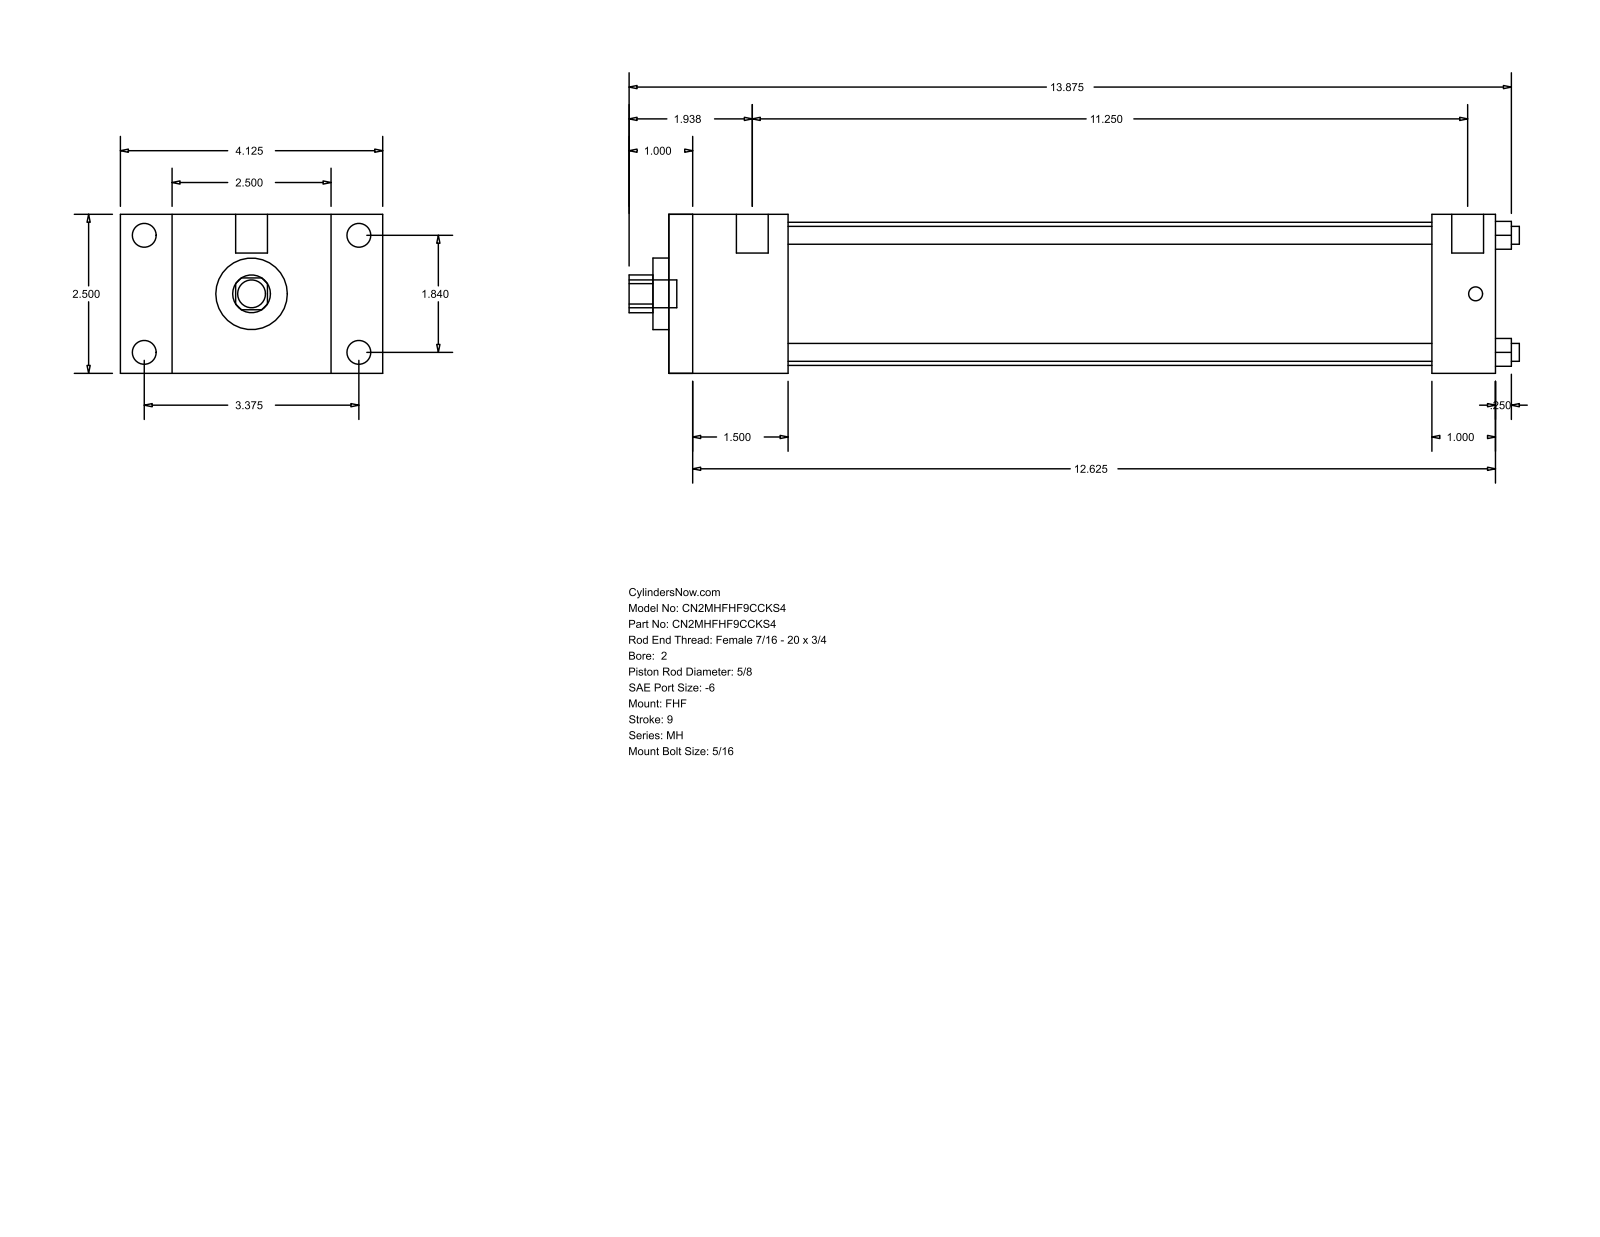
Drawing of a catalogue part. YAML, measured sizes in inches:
part_name: "MH_FHF__0200_0.625"
step_written_by: "GSSL Pune (CONFIG_CONTROL_DESIGN)"
units: inches
bodies: {solids: 0, faces: 88, planar: 60, cylindrical: 28, other: 0}
overall_size: [14, 4.125, 2.5]
round_holes:
  - {diameter: 0.281, count: 4}
  - {diameter: 0.625, count: 1}
  - {diameter: 1.125, count: 1}
  - {diameter: 2.25, count: 1}
round_bosses_or_shafts:
  - {diameter: 0.375, count: 4}
  - {diameter: 0.219, count: 4}
  - {diameter: 0.5, count: 2}
  - {diameter: 0.437, count: 1}
partial_cylinders:
  - {radius: 0.297, count: 1}
face_to_face_distances: [2.5, 1.875, 13, 11.125, 0.813, 3.313, 4.125, 12, 10.125, 1]
hole_center_spacings: [1.301, 1.84, 2.602]
